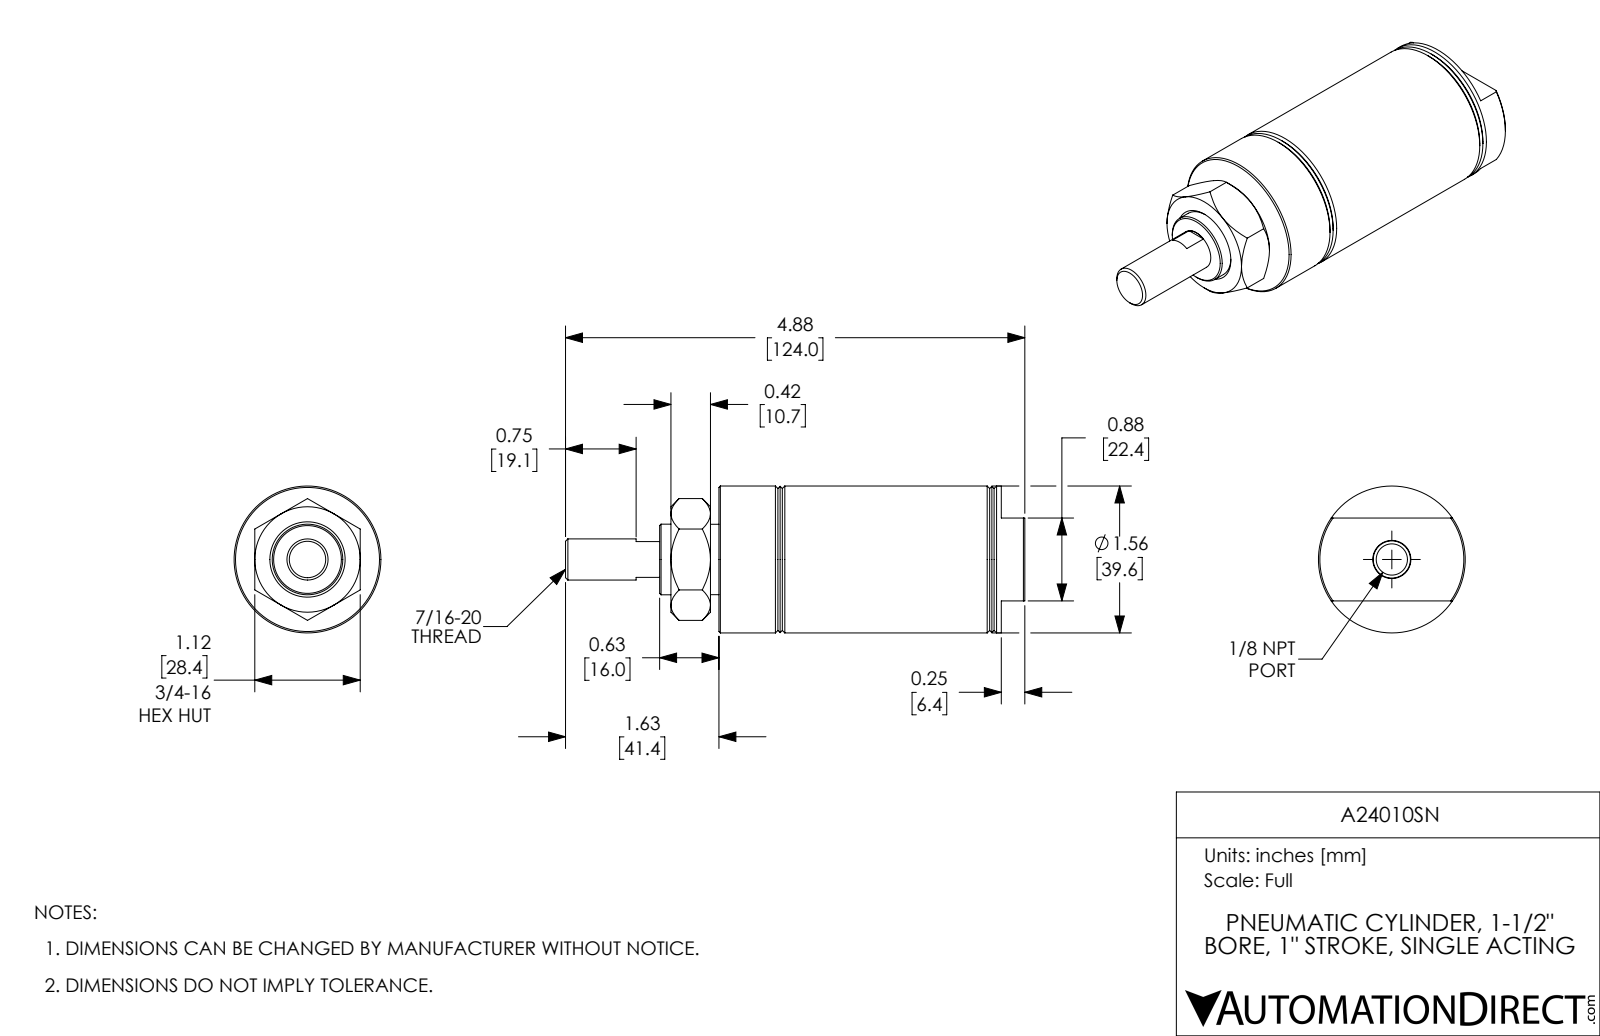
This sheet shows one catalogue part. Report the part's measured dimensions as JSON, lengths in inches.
{"part_name": "A24010SN; A24010SN_Mounting Nut_D-3556; A24010SN-Rod; A24010SN-MainBody", "step_written_by": "SolidWorks 2017 (AUTOMOTIVE_DESIGN)", "units": "inches", "bodies": {"solids": 3, "faces": 93, "planar": 28, "cylindrical": 22, "other": 43}, "overall_size": [4.88, 1.56, 1.56], "volume_in3": 5.034, "surface_area_in2": 48.95, "round_holes": [[0.332, 1], [0.437, 1], [0.75, 1], [1.5, 1]], "round_bosses_or_shafts": [[1.56, 1], [0.747, 1]], "face_to_face_distances": [1, 0.5, 1.5, 2.375, 1.875, 0.875, 0.875, 1.375, 2.375, 3.25]}
